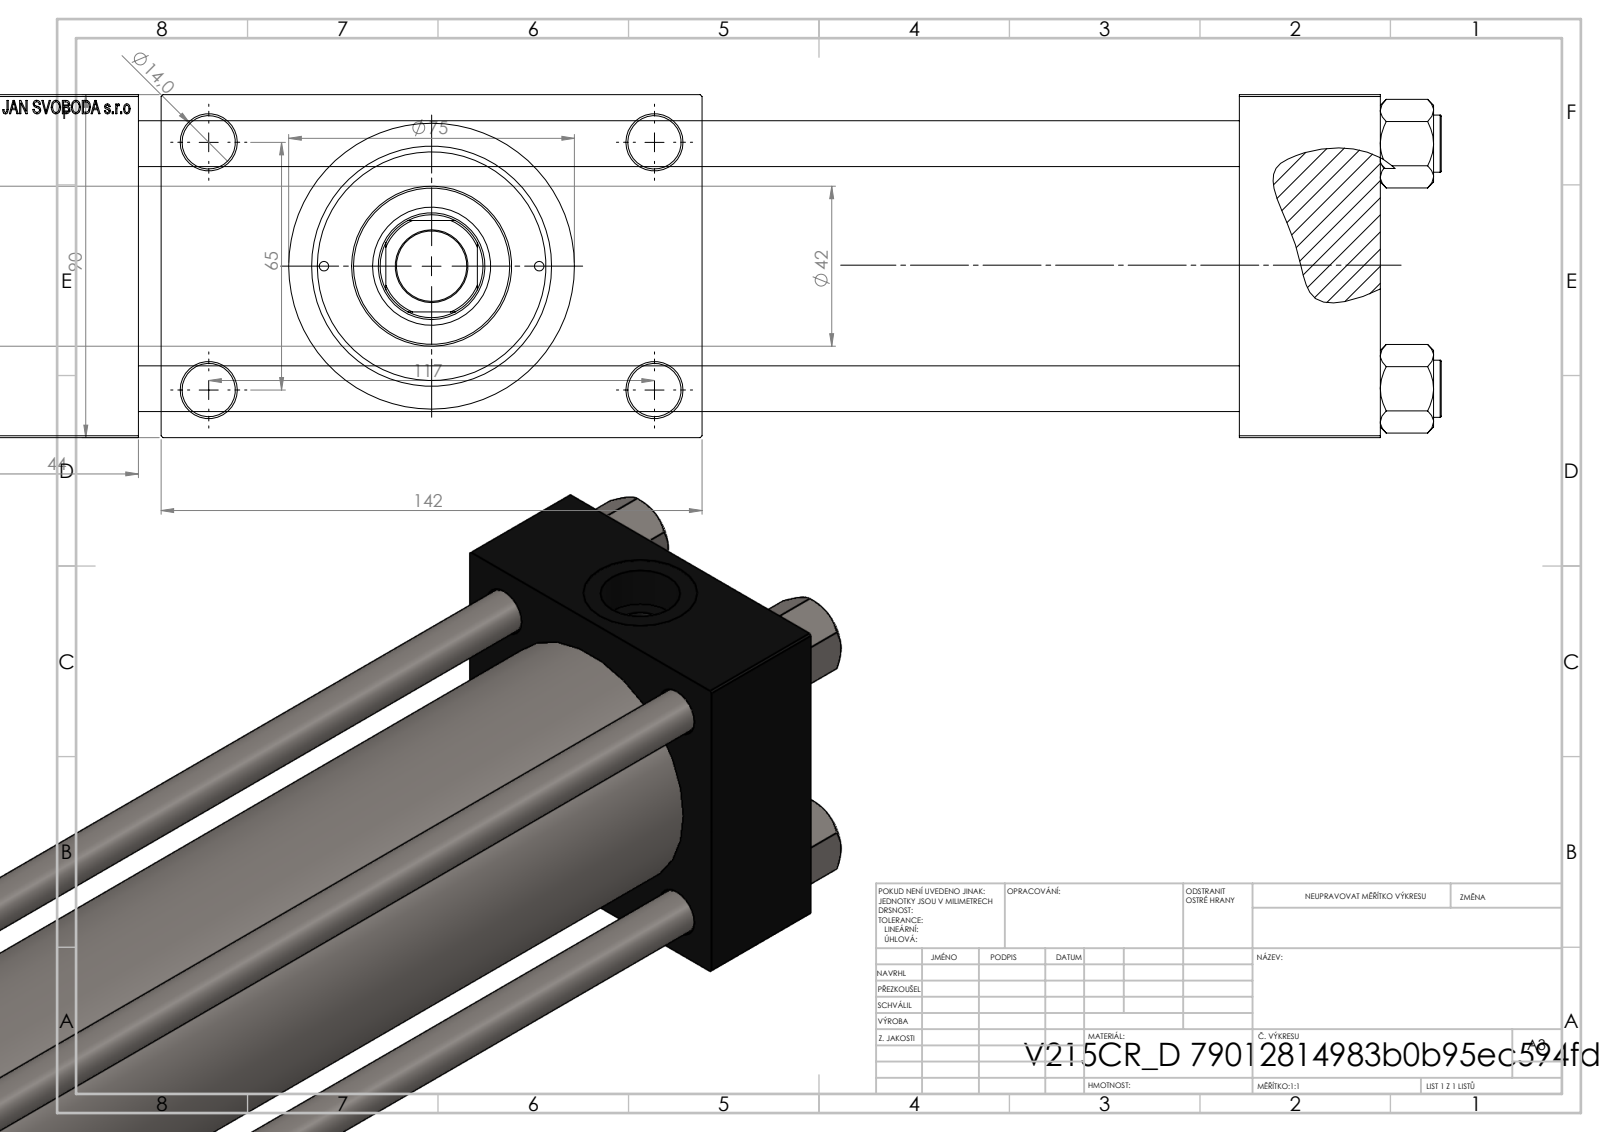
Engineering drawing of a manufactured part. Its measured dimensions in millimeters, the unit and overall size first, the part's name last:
Units: millimetres
Overall size (bounding box): 433 × 142 × 90
Round holes (diameter × count): ⌀12 ×4, ⌀14 ×4, ⌀2.5 ×2, ⌀7 ×2, ⌀20.96 ×2, ⌀30 ×2, ⌀18.5 ×1, ⌀28 ×1, ⌀31 ×1, ⌀50 ×1, ⌀60 ×1, ⌀63 ×1
Round bosses / shafts (diameter × count): ⌀15 ×4, ⌀75 ×1, ⌀69 ×1, ⌀42 ×1
Partial cylindrical surfaces — rounded edges, fillets, slot ends (radius × count): R13.5 ×1
Main face-to-face distances: 90, 289, 37, 326, 333, 370, 44, 26, 116, 142
Hole centre spacings: 26.35, 32.39, 44.4, 45.47, 64.3, 66.92, 68.42, 69.81
Volume: 1 494 000 mm³ · Surface area: 348 817 mm²
Bodies: 11 solids, 1112 faces (499 planar, 93 cylindrical, 520 other)
Part name (STEP PRODUCT): V215CR_D_Body; V215CR_VCP_D; V215CR_D_TYCINKA; NUT_M5_D (+1 more)
STEP written by: SolidWorks 2019 (CONFIG_CONTROL_DESIGN)
